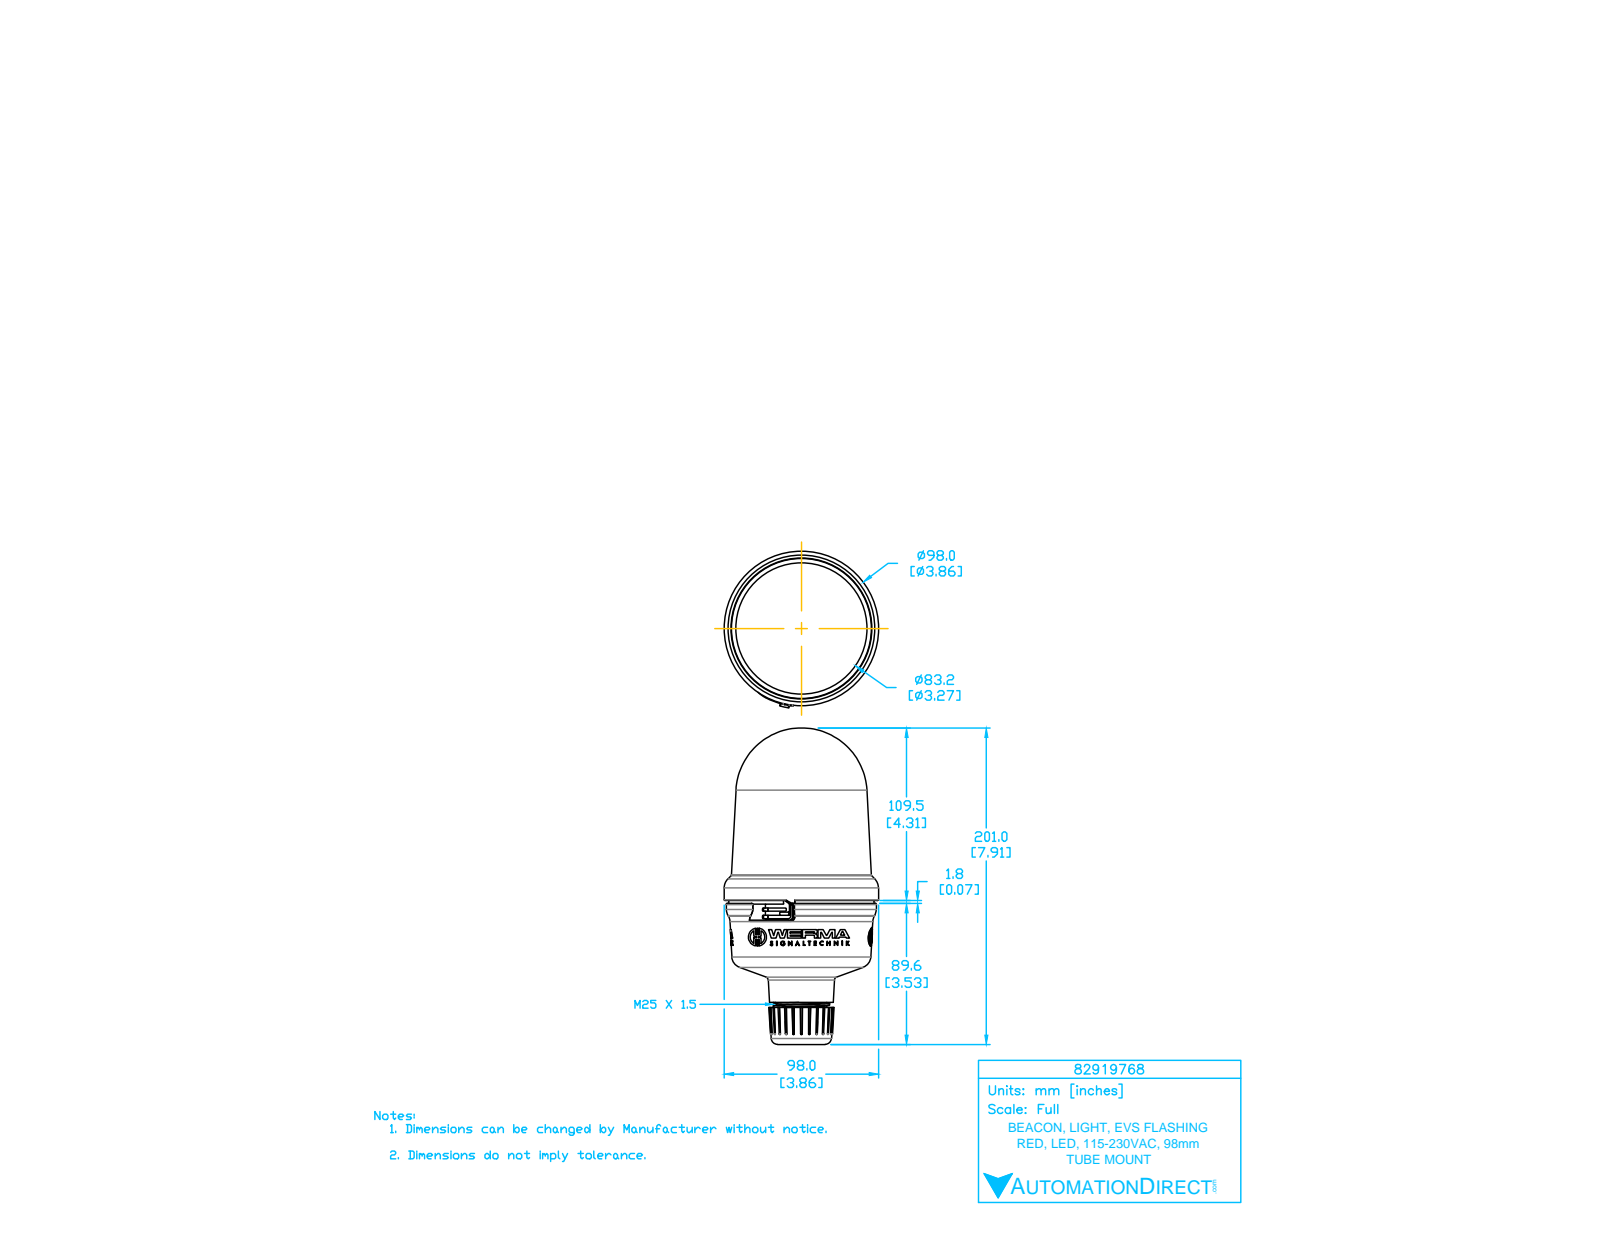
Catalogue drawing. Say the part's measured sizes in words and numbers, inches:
The part is named "82919768". Its 3-D file was written by "SolidWorks 2015 (AUTOMOTIVE_DESIGN)". It is 1 solid with 1006 faces: 554 planar, 189 cylindrical and 263 other. Overall it measures 7.914 by 3.912 by 3.858 inches. Its volume is 54.7 cubic inches and its surface area 91.39 square inches. Round holes: 3 of diameter 0.078, 1 of diameter 1.013, 1 of diameter 1.024. Round bosses or shafts: 3 of diameter 0.452, 3 of diameter 0.113, 1 of diameter 3.858, 1 of diameter 1.409, 1 of diameter 1.261. Partial cylindrical surfaces (rounded edges, fillets, slot ends): 12 of radius 0.02, 9 of radius 0.007, 6 of radius 0.007, 6 of radius 0.016, 6 of radius 0.016, 6 of radius 0.016, 6 of radius 0.262, 3 of radius 0.006. The main face-to-face distances are 2.214, 0.462, 2.676, 0.335, 0.127, 2.548, 2.603, 2.476, 2.141, 0.073.
